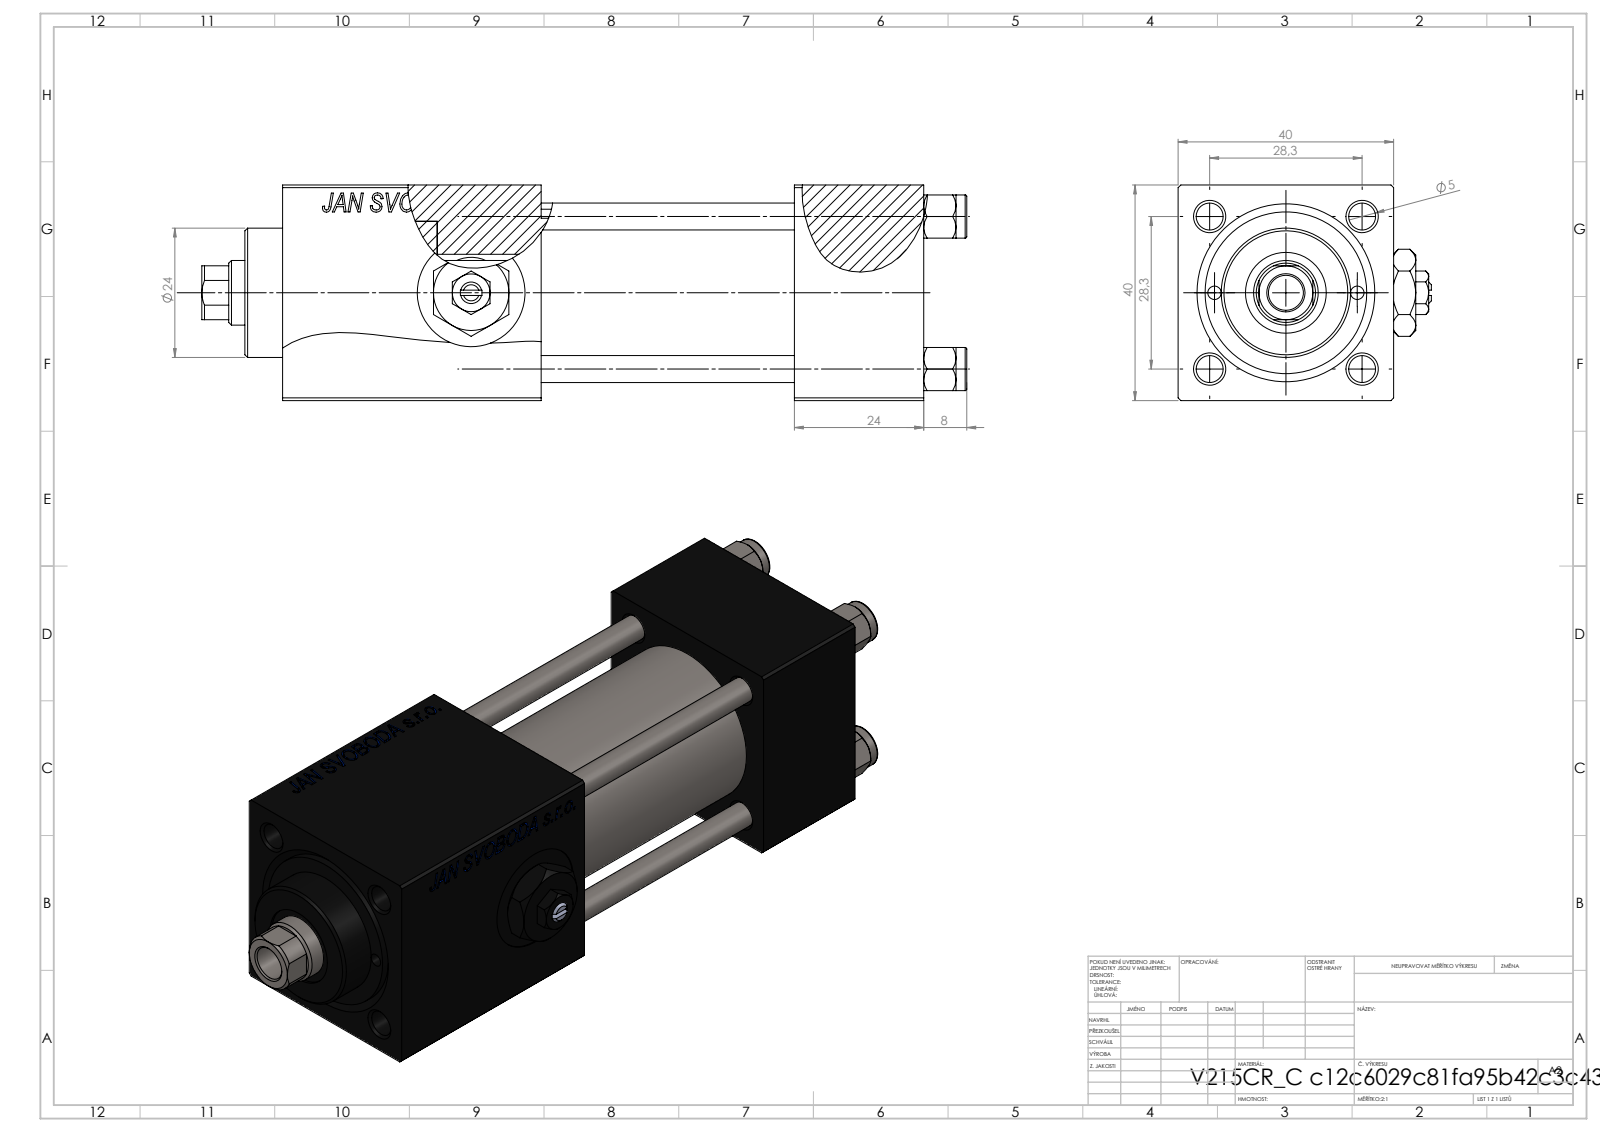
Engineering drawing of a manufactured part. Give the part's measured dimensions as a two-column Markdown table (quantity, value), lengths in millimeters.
| quantity | value |
| --- | --- |
| part name | V215CR_VCP_C; Zatka_pro_OIL_PORT; V215_VC_A; V215CR_C_TYCINKA (+2 more) |
| STEP written by | SolidWorks 2019 (CONFIG_CONTROL_DESIGN) |
| units | millimeters |
| bodies | 12 solids, 1201 faces (551 planar, 94 cylindrical, 556 other) |
| overall size | 142 × 47 × 40 |
| volume | 141 689 mm³ |
| surface area | 55 264 mm² |
| round holes (diameter × count) | 5 × 4, 20 × 3, 2.5 × 2, 7 × 2, 13.16 × 2, 6.5 × 1, 12 × 1, 15 × 1, 25 × 1, 30 × 1 |
| round bosses / shafts (diameter × count) | 8 × 4, 31 × 1, 24 × 1 |
| partial cylindrical surfaces (radius × count) | 5.5 × 1 |
| main face-to-face distances | 40, 24, 90.3, 66.3, 48, 47, 71, 19.3, 119, 95 |
| hole center spacings | 14.18, 20.01, 28.3, 30.84, 13.25, 40.02, 26.5, 72 |
